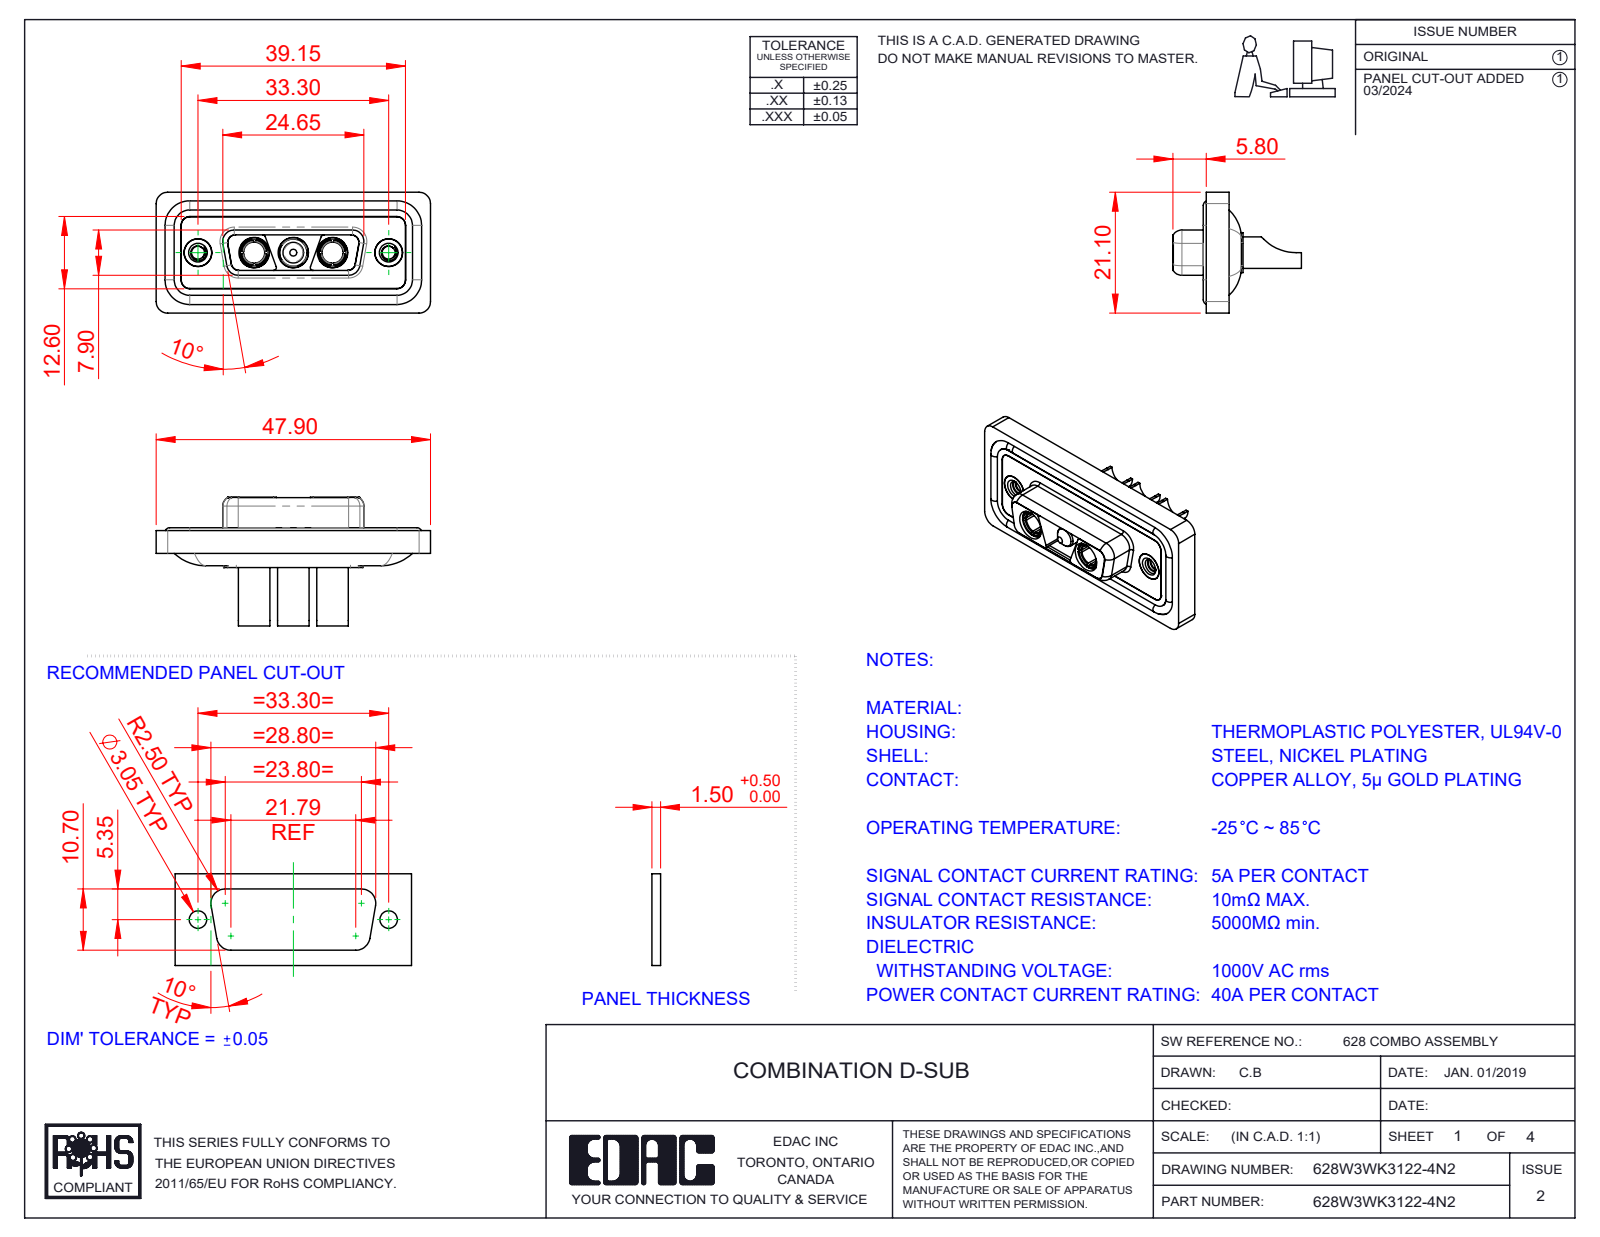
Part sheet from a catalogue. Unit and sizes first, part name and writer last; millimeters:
Units: millimetres
Overall size (bounding box): 47.9 × 22.45 × 21.1
Round holes (diameter × count): ⌀4.85 ×5, ⌀4.6 ×3, ⌀5.3 ×3, ⌀2.26 ×2, ⌀3.7 ×2, ⌀4 ×2, ⌀4.05 ×2, ⌀5 ×2
Round bosses / shafts (diameter × count): ⌀1.6 ×4, ⌀5.5 ×3, ⌀5.2 ×3, ⌀4.75 ×3, ⌀3.75 ×3, ⌀4.96 ×2, ⌀4.95 ×2, ⌀4.8 ×2
Partial cylindrical surfaces — rounded edges, fillets, slot ends (radius × count): R1.5 ×22, R2 ×20, R1.35 ×12, R0.5 ×8, R1.6 ×8, R0.25 ×4, R0.6 ×4, R0.65 ×4
Main face-to-face distances: 0.4, 1.6, 0.5, 1.1, 2.9, 5.65, 1.8, 7.05, 5.35, 6.6
Hole centre spacings: 6.85, 9.8, 16.65, 23.5, 13.7, 33.3
Volume: 5 998 mm³ · Surface area: 9 924 mm²
Bodies: 13 solids, 593 faces (184 planar, 261 cylindrical, 148 other)
Part name (STEP PRODUCT): 628Combo Shell Rear_15 Contacts; 628Combo Waterproof Housing_15 Contacts; Power Pin_40A SC; 628Combo Shell Front_15 Contacts (+4 more)
STEP written by: SolidWorks 2023 (CONFIG_CONTROL_DESIGN)
